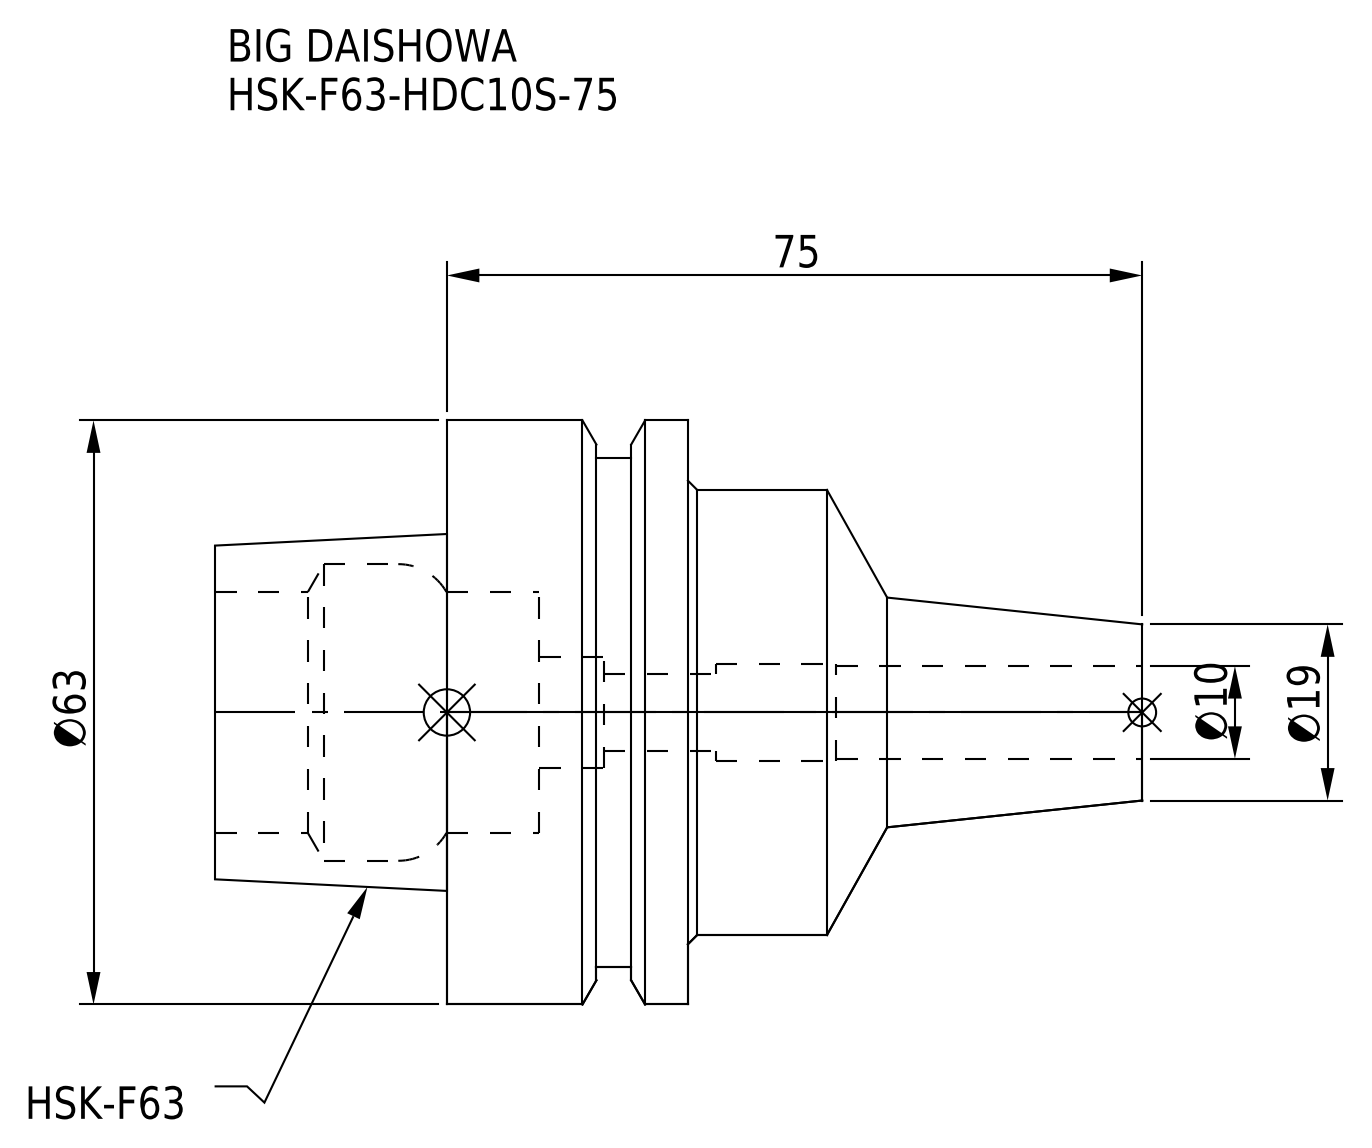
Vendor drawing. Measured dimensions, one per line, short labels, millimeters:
name: HSK-F63-HDC10S-75
written by: CREO PARAMETRIC BY PTC INC, 2016380 (AUTOMOTIVE_DESIGN)
unit: mm
bodies: 1 solid, 50 faces (10 planar, 24 cylindrical, 16 other)
size: 100 × 63 × 63
volume: 122 265 mm³; area: 24 479 mm²
holes: 1× ⌀8.25, 1× ⌀10, 1× ⌀10.5, 1× ⌀12, 1× ⌀26, 1× ⌀32
bosses: 1× ⌀63, 1× ⌀55, 1× ⌀48
face distances: 26, 51, 25, 16.05, 9.95, 34.95, 6.12, 9.93, 19.88, 44.88
